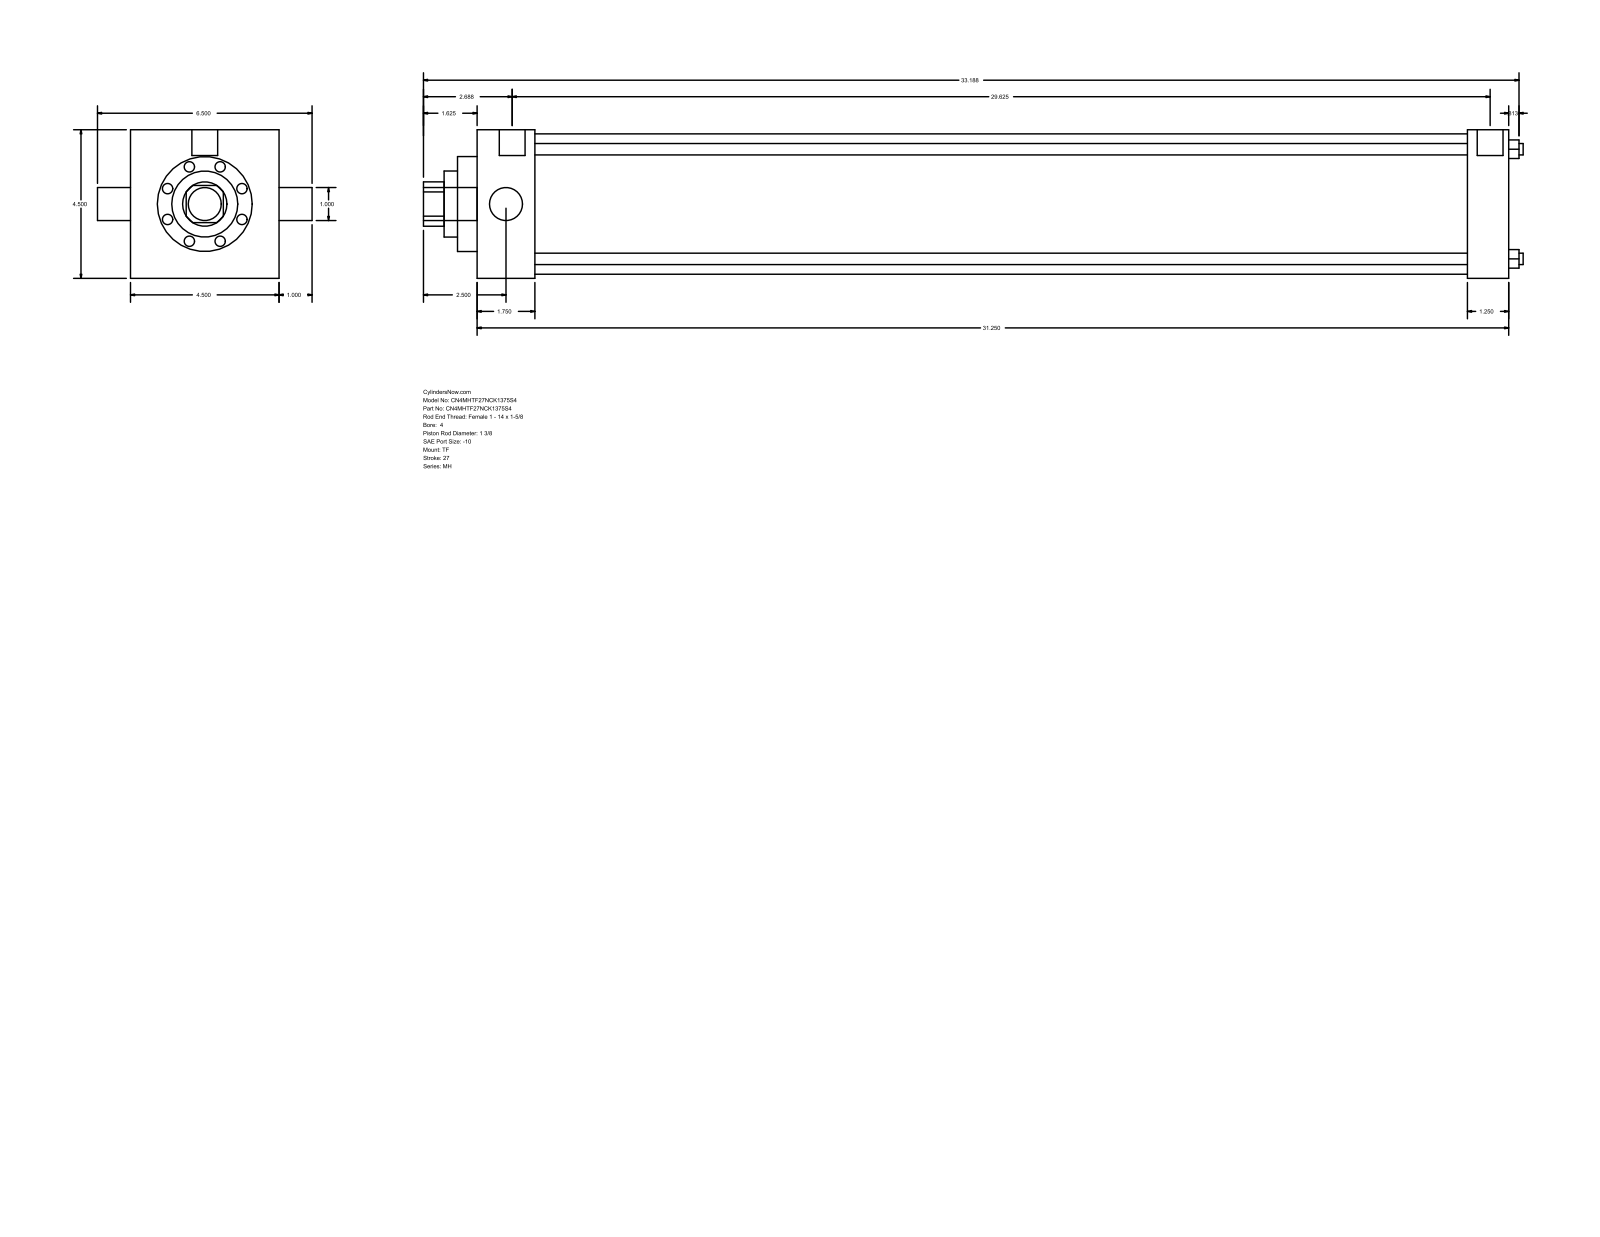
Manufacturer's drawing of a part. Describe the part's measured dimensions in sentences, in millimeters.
The part is named "MH_TF__0400_1.375". Its 3-D file was written by "GSSL Pune (CONFIG_CONTROL_DESIGN)". It is 0 solids with 86 faces: 61 planar, 25 cylindrical and 0 other. Overall it measures 846.14 by 165.1 by 114.3 millimeters. Round holes: 4 of diameter 8.76, 1 of diameter 25.4, 1 of diameter 34.92, 1 of diameter 50.8, 1 of diameter 73.03, 1 of diameter 107.95. Round bosses or shafts: 3 of diameter 8.73, 2 of diameter 19.84, 1 of diameter 25.4. Partial cylindrical surfaces (rounded edges, fillets, slot ends): 1 of radius 17.06. The main face-to-face distances are 114.3, 793.75, 44.45, 749.3, 762, 717.55, 31.75, 15.08, 59.53, 777.08. The hole center spacings are 59.62, 84.32, 119.25.
